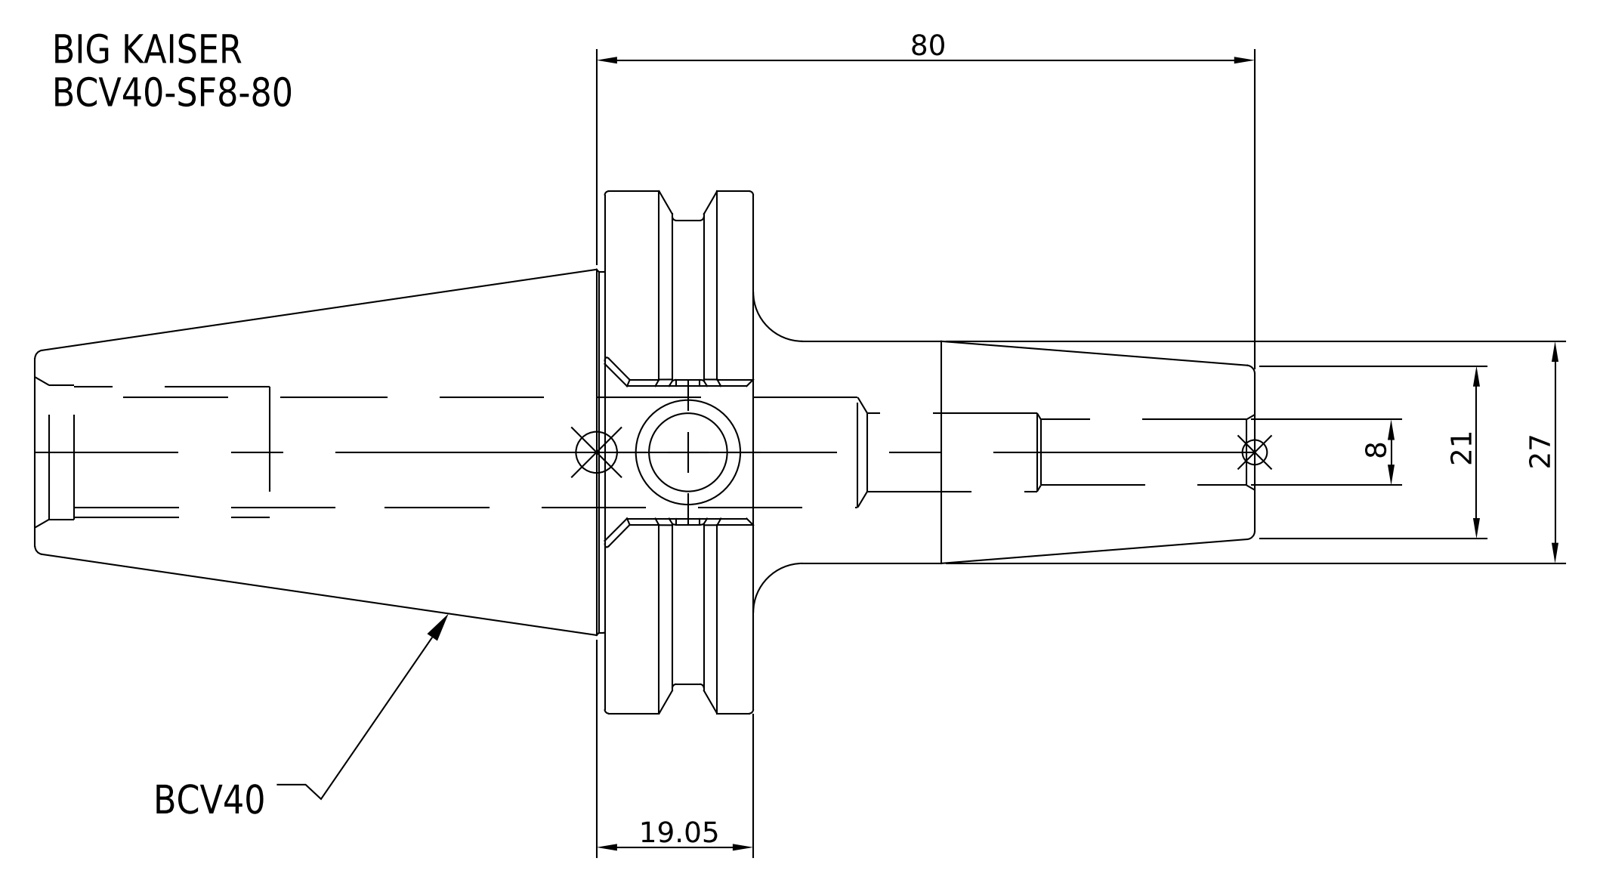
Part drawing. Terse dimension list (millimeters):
name: BCV40-SF8-80
written by: SolidWorks 2021 (CONFIG_CONTROL_DESIGN)
unit: mm
bodies: 1 solid, 27 faces (7 planar, 12 cylindrical, 8 other)
size: 148.25 × 63.5 × 63.5
volume: 149 928 mm³; area: 22 501 mm²
holes: 1× ⌀8
bosses: 1× ⌀63.5, 1× ⌀56.36, 1× ⌀44.45, 1× ⌀27
face distances: 18.05, 87.3, 69.25, 60.95, 79, 148.25, 66.95, 6, 12.05, 81.3
